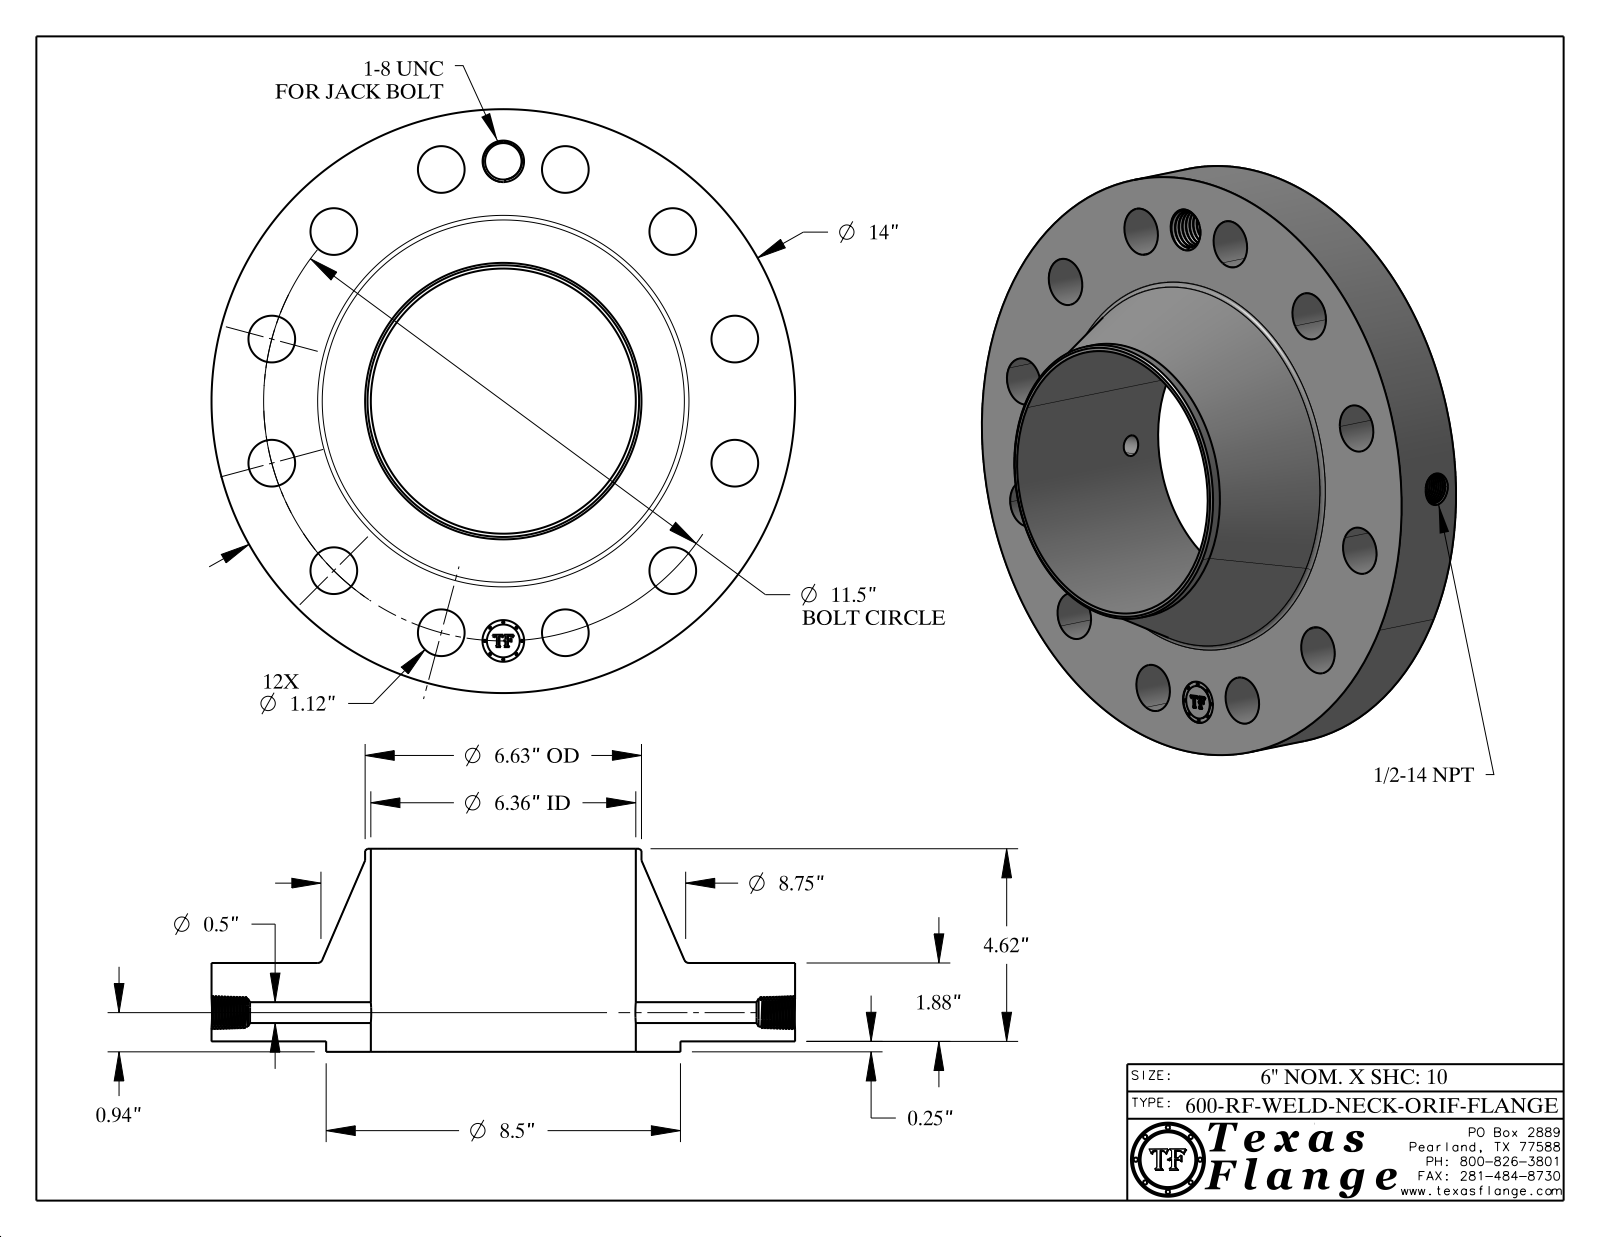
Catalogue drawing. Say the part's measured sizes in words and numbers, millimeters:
The part is named "600-RF-WELD-NECK". Its 3-D file was written by "CATIA V5 STEP AP214 (AUTOMOTIVE_DESIGN)". It is 1 solid with 779 faces: 369 planar, 101 cylindrical and 309 other. Overall it measures 355.6 by 355.6 by 123.7 millimeters. Its volume is 4 067 000 cubic millimeters and its surface area 356 500 square millimeters. Round holes: 12 of diameter 28.4, 1 of diameter 12.7, 1 of diameter 17.1, 1 of diameter 22.2, 1 of diameter 25.4, 1 of diameter 161.5. Round bosses or shafts: 8 of diameter 1.5, 1 of diameter 355.6, 1 of diameter 215.9, 1 of diameter 168.4, 1 of diameter 20. The main face-to-face distances are 47.8, 6.4, 54.1, 123.7, 117.3, 69.6, 53.7, 47.4, 0.4, 70. The hole center spacings are 146.1, 75.6, 206.5, 253, 282.1, 292.1, 38.1, 111.8.
